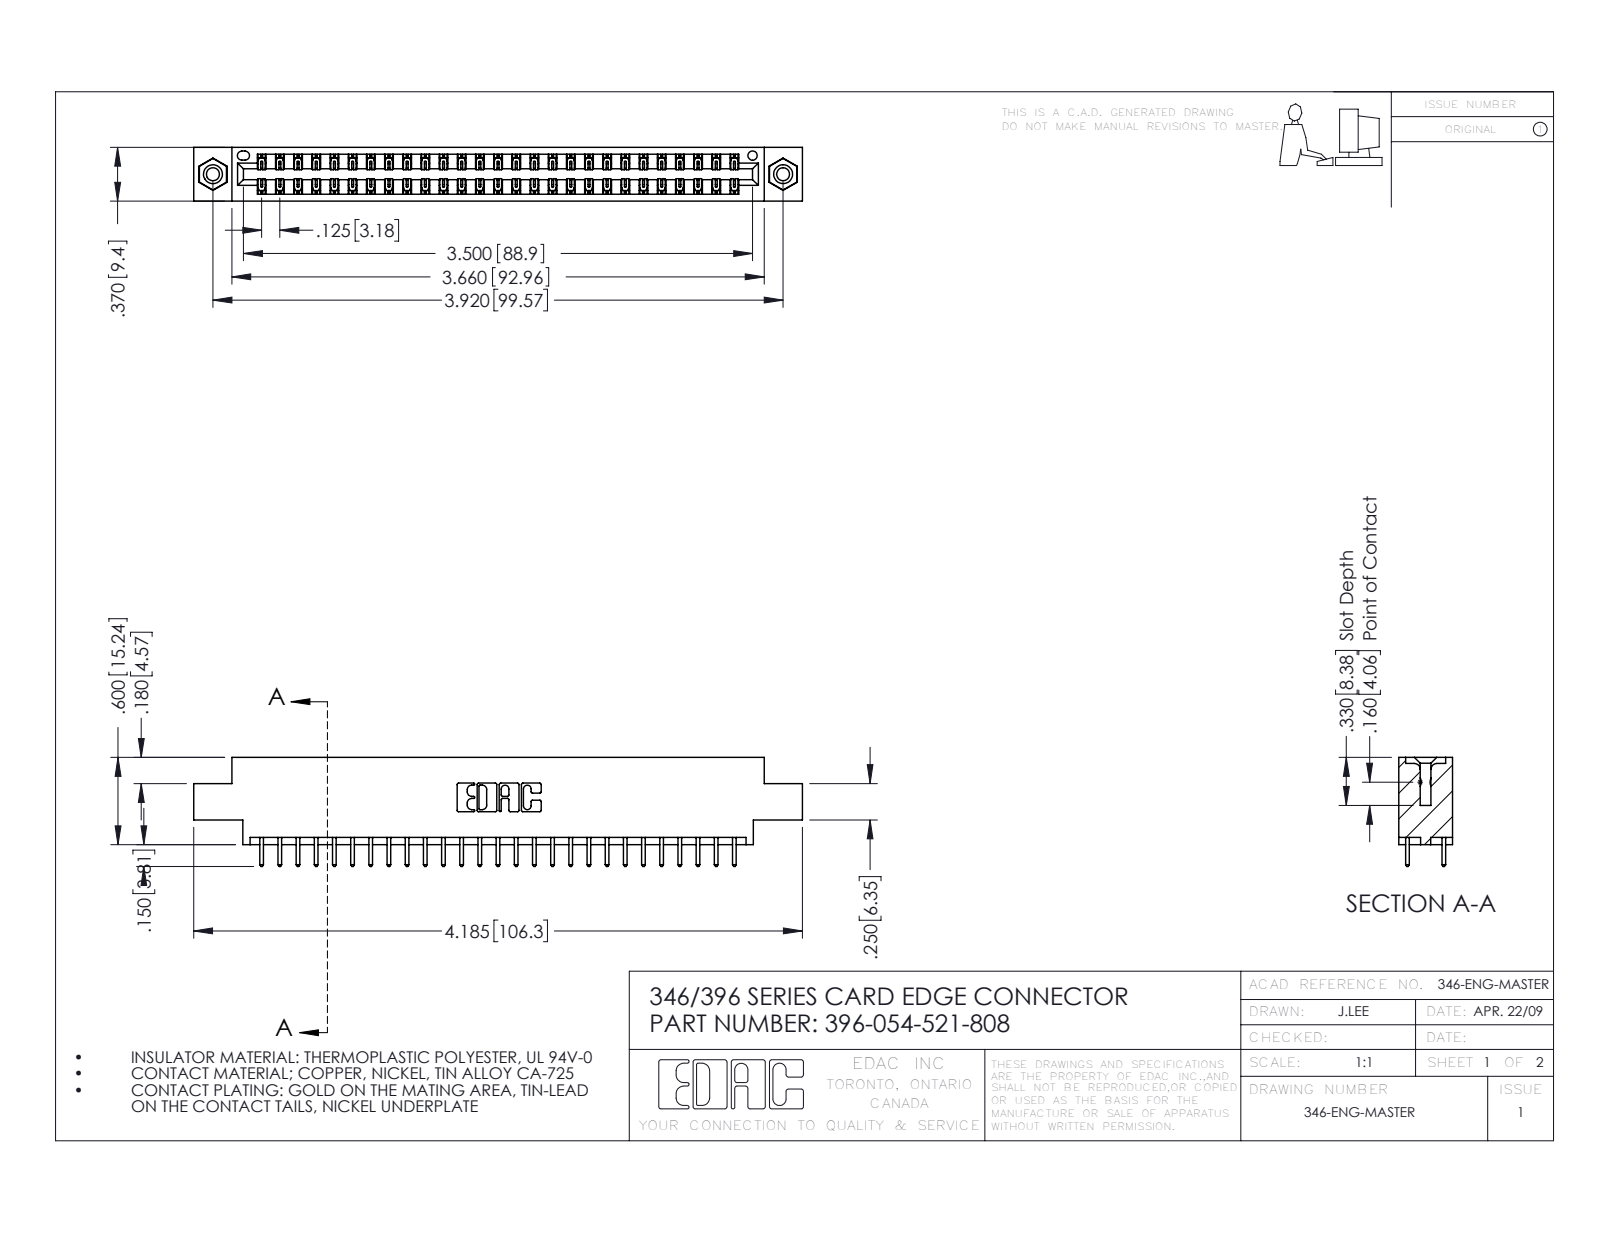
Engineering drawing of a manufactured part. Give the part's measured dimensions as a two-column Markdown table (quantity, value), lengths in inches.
| quantity | value |
| --- | --- |
| part name | 346 Part_0.170 Offset - 0.156 Dia-TI; 345-292-001_345-293-121; 396-054-521-808; 345-250-001_345-250-003-102 |
| STEP written by | SolidWorks 2016 (CONFIG_CONTROL_DESIGN) |
| units | inches |
| bodies | 57 solids, 2994 faces (2002 planar, 976 cylindrical, 16 other) |
| overall size | 4.185 × 0.75 × 0.37 |
| volume | 0.614 in³ |
| surface area | 21.16 in² |
| round holes (diameter × count) | 0.089 × 2, 0.125 × 2, 0.156 × 2, 0.064 × 1 |
| round bosses / shafts (diameter × count) | 0.155 × 2 |
| partial cylindrical surfaces (radius × count) | 0.006 × 81, 0.01 × 54, 0.01 × 22, 0.007 × 6, 0.031 × 6, 0.026 × 3, 0.014 × 2, 0.022 × 2 |
| main face-to-face distances | 0.048, 0.322, 0.37, 0.25, 0.072, 0.298, 0.025, 0.275, 0.222, 0.148 |
| hole center spacings | 0.246, 3.712, 3.92 |
